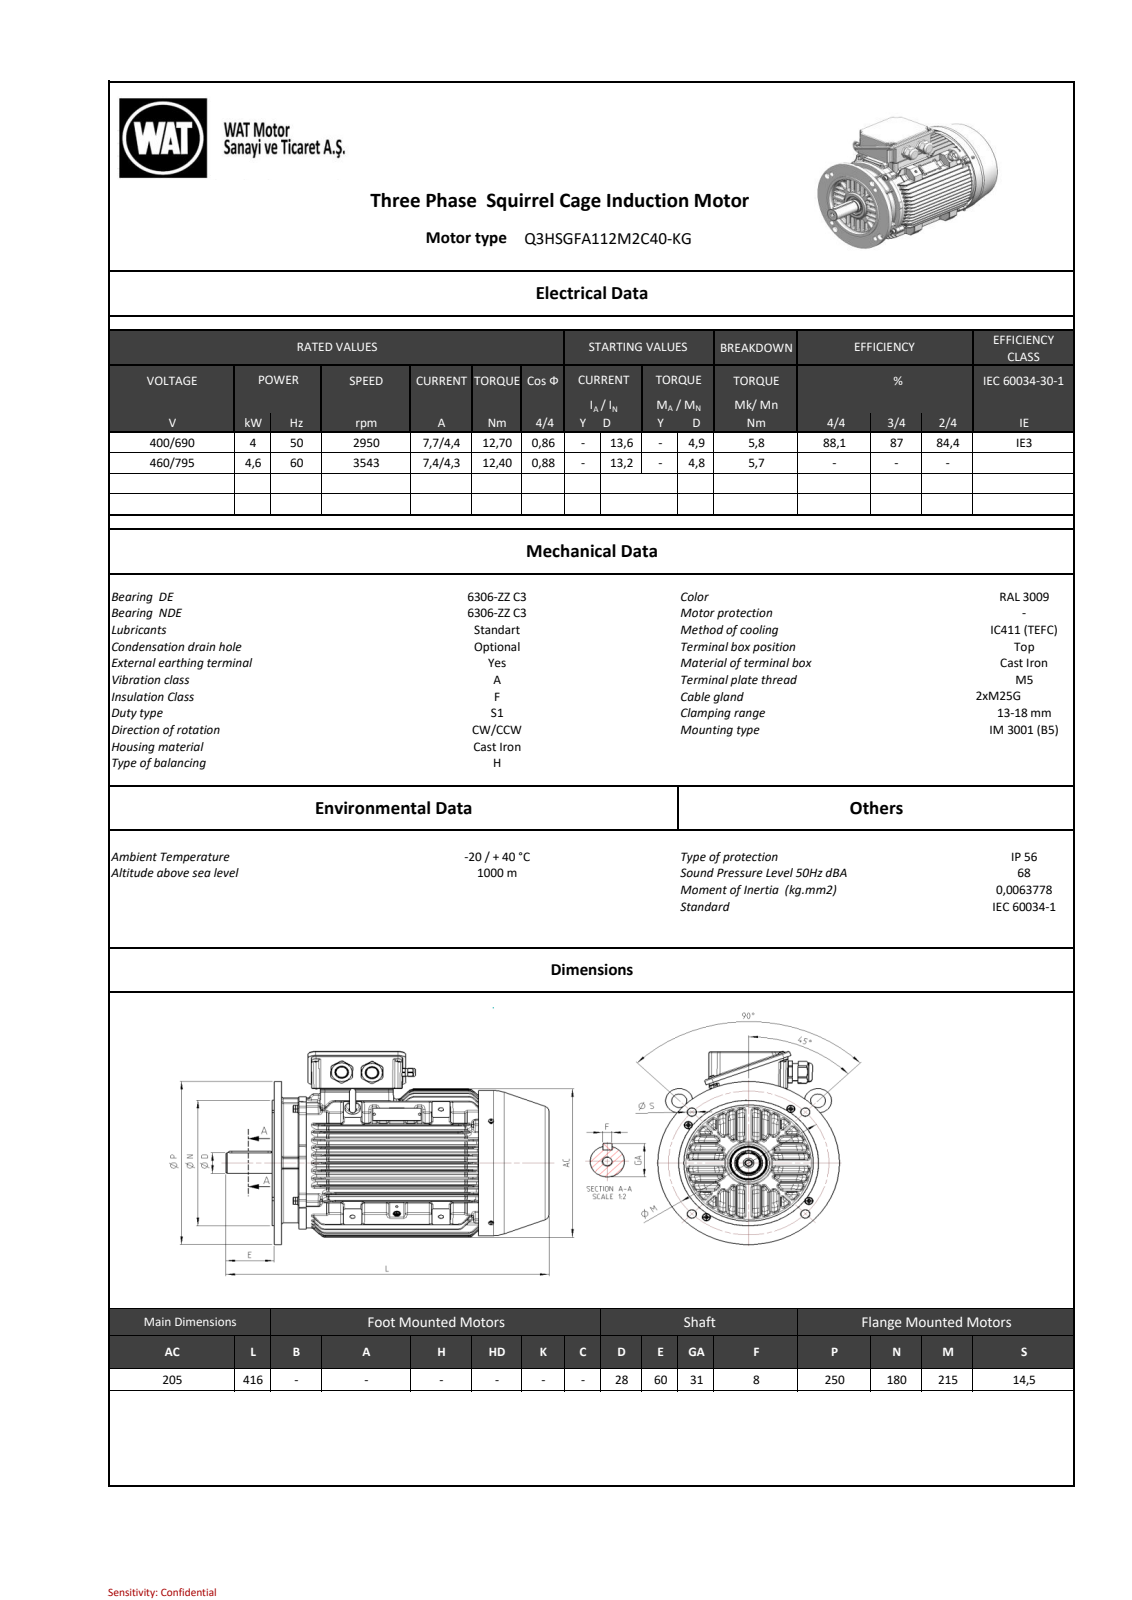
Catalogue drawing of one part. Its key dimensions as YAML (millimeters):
part_name: "260037F440EAova6"
step_written_by: "SIEMENS PLM Software NX 11.0 (AUTOMOTIVE_DESIGN)"
units: millimeters
bodies: {solids: 0, faces: 4093, planar: 780, cylindrical: 993, other: 2320}
overall_size: [408, 295.48, 250]
round_holes:
  - {diameter: 5, count: 8}
  - {diameter: 6.8, count: 6}
  - {diameter: 11, count: 4}
  - {diameter: 10, count: 3}
  - {diameter: 2.5, count: 2}
  - {diameter: 4.2, count: 2}
  - {diameter: 6.5, count: 1}
  - {diameter: 6.6, count: 1}
  - {diameter: 8.5, count: 1}
  - {diameter: 10.5, count: 1}
  - {diameter: 43.4, count: 1}
  - {diameter: 43.6, count: 1}
round_bosses_or_shafts:
  - {diameter: 10, count: 4}
  - {diameter: 8.65, count: 4}
  - {diameter: 8, count: 4}
  - {diameter: 4, count: 3}
  - {diameter: 31.6, count: 2}
  - {diameter: 20, count: 2}
  - {diameter: 12, count: 2}
  - {diameter: 250, count: 1}
partial_cylinders:
  - {radius: 4, count: 249}
  - {radius: 1.5, count: 118}
  - {radius: 3, count: 71}
  - {radius: 2, count: 29}
  - {radius: 1.8, count: 23}
  - {radius: 1, count: 22}
  - {radius: 0.25, count: 18}
  - {radius: 26.5, count: 12}
face_to_face_distances: [13.53, 27.15, 13.62, 40.84, 27.31, 13.69, 78.83, 65.21, 51.68, 54.62]
hole_center_spacings: [89.5, 126.57, 58.5, 71.5, 31.07, 102.68, 130, 146.62]
